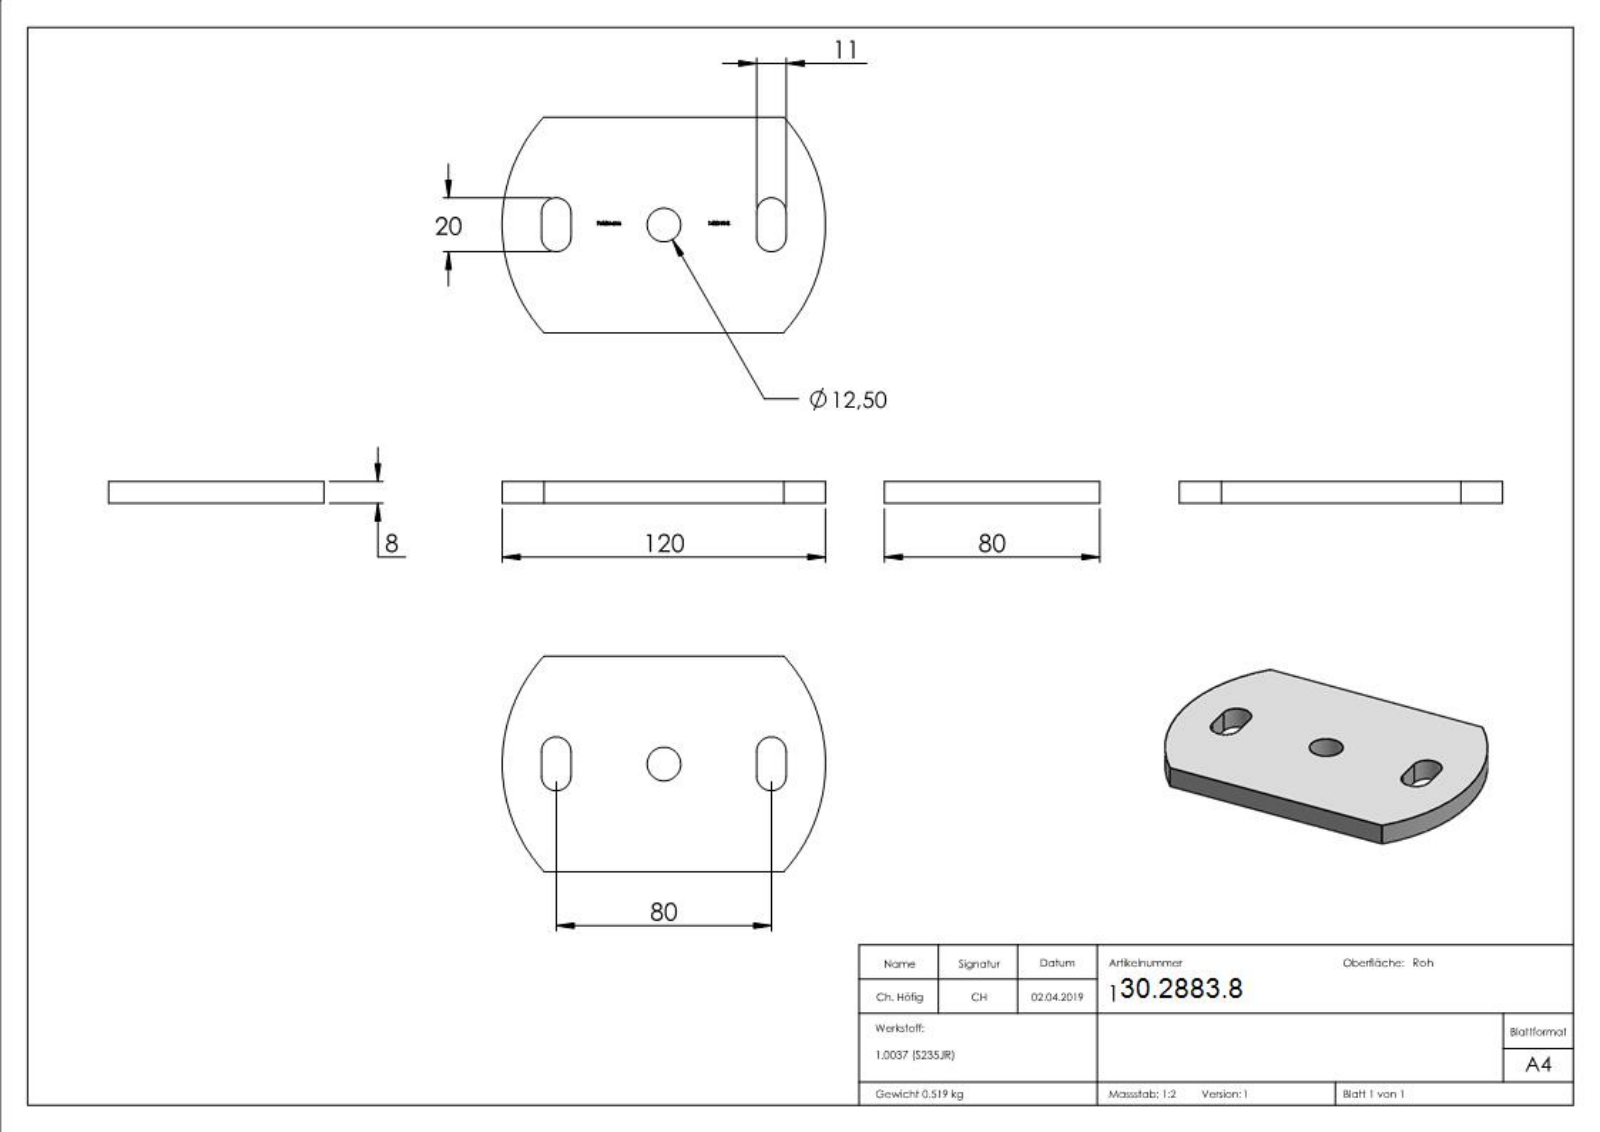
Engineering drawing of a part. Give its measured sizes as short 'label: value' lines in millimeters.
name: 1422-W-8
written by: SolidWorks 2015 (CONFIG_CONTROL_DESIGN)
unit: mm
bodies: 1 solid, 223 faces (136 planar, 10 cylindrical, 77 other)
size: 120 × 80 × 8
volume: 66 489 mm³; area: 20 615 mm²
holes: 1× ⌀12.5
rounds: 4× R5.5, 2× R59.36
face distances: 8, 80, 11, 91, 69, 7.9, 40, 0.44, 39.47, 2.02
